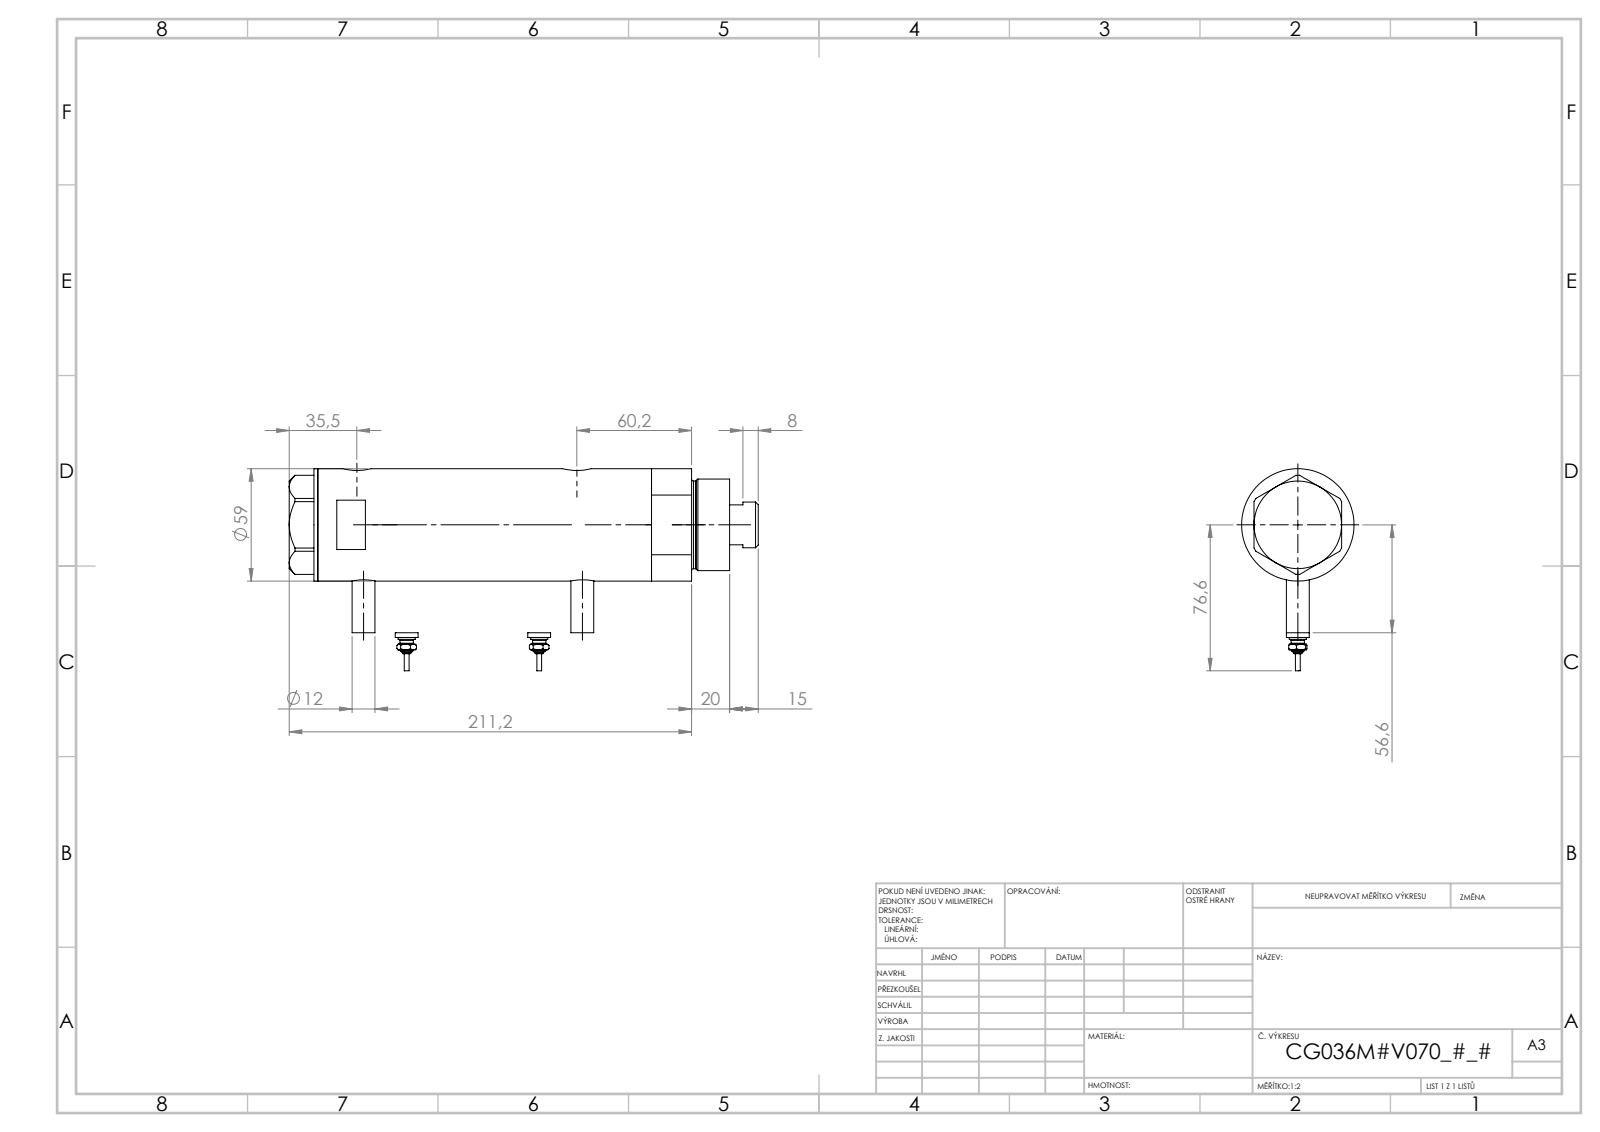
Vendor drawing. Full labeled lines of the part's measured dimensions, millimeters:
Part name (STEP PRODUCT): V270CG_SWITCH; V270CG_BACK; V270CG_VC; V270CG_MIDDLE (+1 more)
STEP written by: SolidWorks 2019 (CONFIG_CONTROL_DESIGN)
Units: millimetres
Bodies: 6 solids, 232 faces (81 planar, 77 cylindrical, 74 other)
Overall size (bounding box): 233.42 × 91.3 × 59
Volume: 528 486 mm³ · Surface area: 110 229 mm²
Round holes (diameter × count): ⌀5 ×2, ⌀9.73 ×2, ⌀12.5 ×2, ⌀15 ×2, ⌀8.5 ×1, ⌀25 ×1, ⌀26.5 ×1, ⌀36 ×1, ⌀40 ×1, ⌀52 ×1
Round bosses / shafts (diameter × count): ⌀12 ×4, ⌀9 ×2, ⌀7 ×2, ⌀4.34 ×2, ⌀2.4 ×2, ⌀59 ×1, ⌀48 ×1, ⌀46 ×1
Main face-to-face distances: 127.34, 23.5, 103.84, 15, 38.5, 142.34, 218.42, 203.42, 179.92, 76.08
Hole centre spacings: 2.9, 3.5, 102.15, 105.05, 105.65, 108.55, 2.89, 2.91
